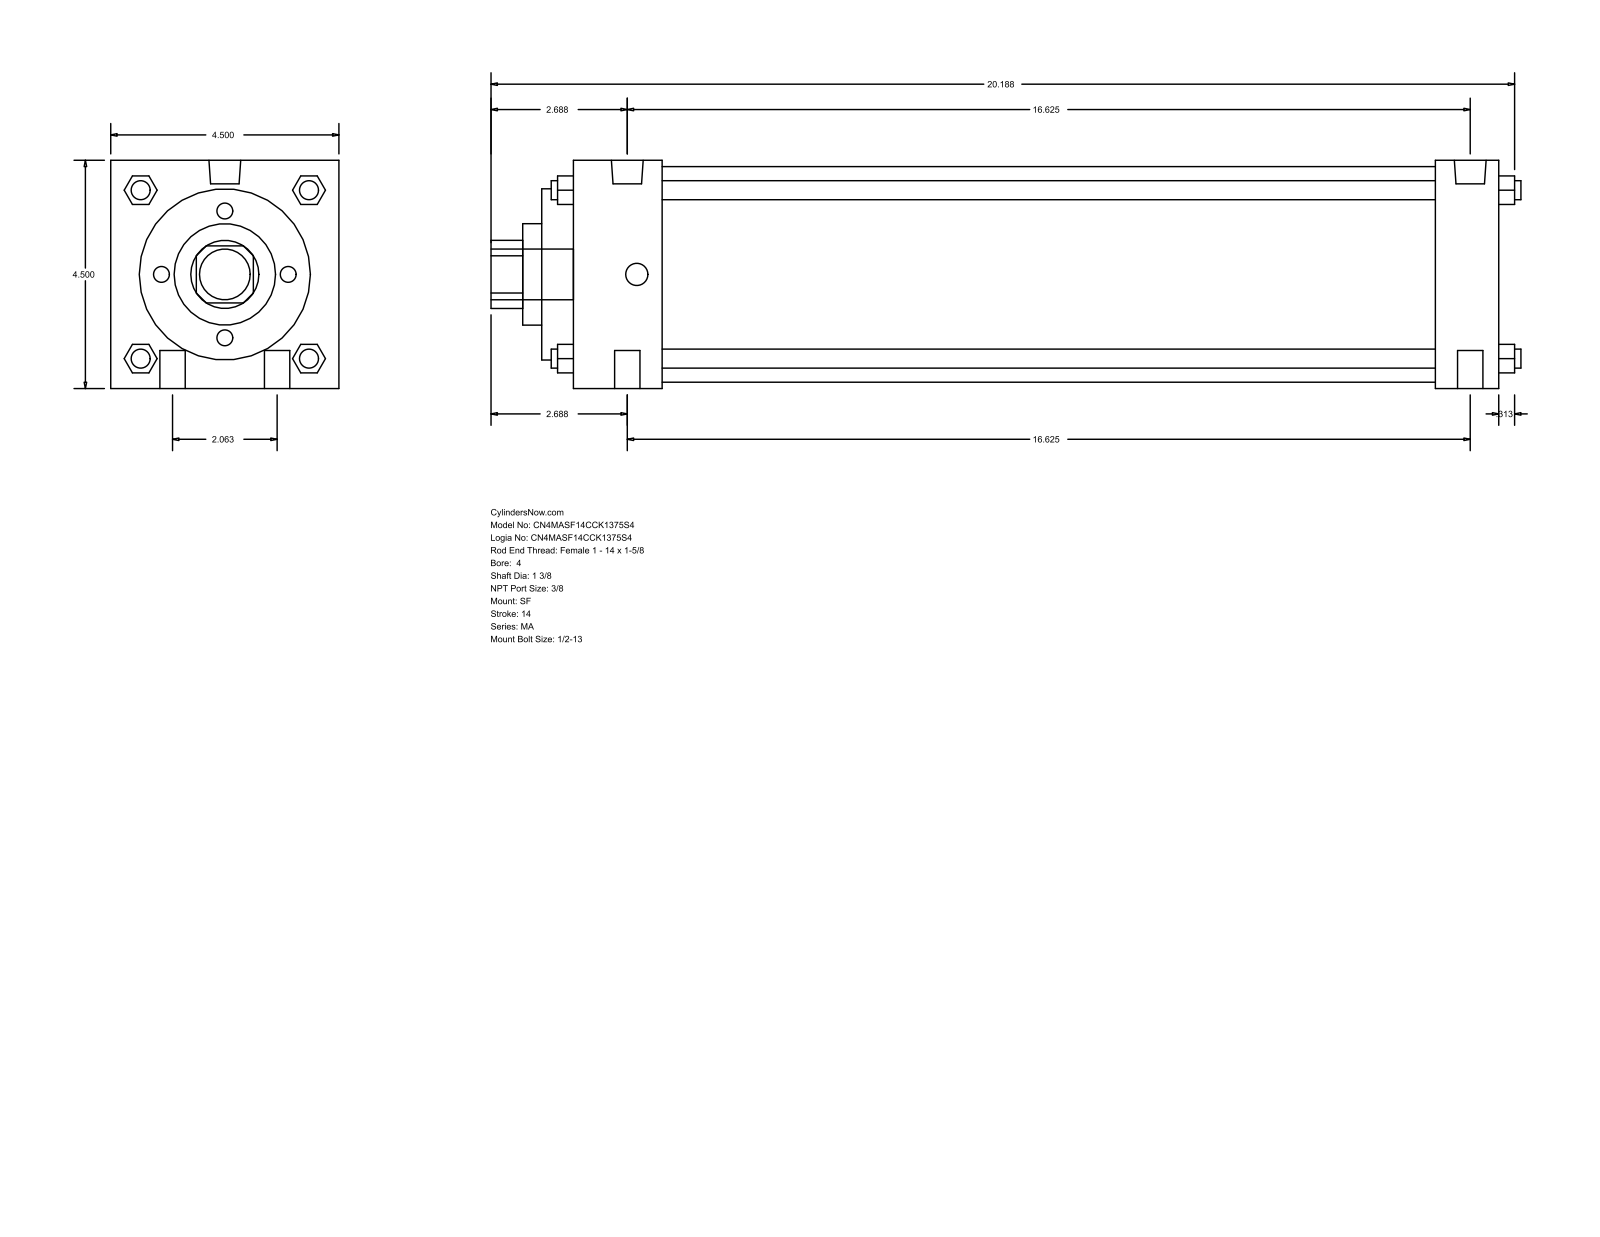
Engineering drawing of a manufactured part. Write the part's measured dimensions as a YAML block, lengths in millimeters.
part_name: "MA_SF__0400_1.375"
step_written_by: "GSSL Pune (CONFIG_CONTROL_DESIGN)"
units: millimeters
bodies: {solids: 0, faces: 126, planar: 95, cylindrical: 31, other: 0}
overall_size: [515.94, 114.3, 114.3]
round_holes:
  - {diameter: 34.92, count: 1}
  - {diameter: 50.8, count: 1}
  - {diameter: 85.72, count: 1}
  - {diameter: 107.95, count: 1}
round_bosses_or_shafts:
  - {diameter: 12.7, count: 4}
  - {diameter: 9.53, count: 4}
  - {diameter: 15.93, count: 2}
  - {diameter: 11.11, count: 2}
  - {diameter: 25.4, count: 1}
partial_cylinders:
  - {radius: 17.06, count: 1}
face_to_face_distances: [114.3, 463.55, 479.42, 15.87, 447.67, 431.8, 31.75, 60.32, 44.45, 387.35]
